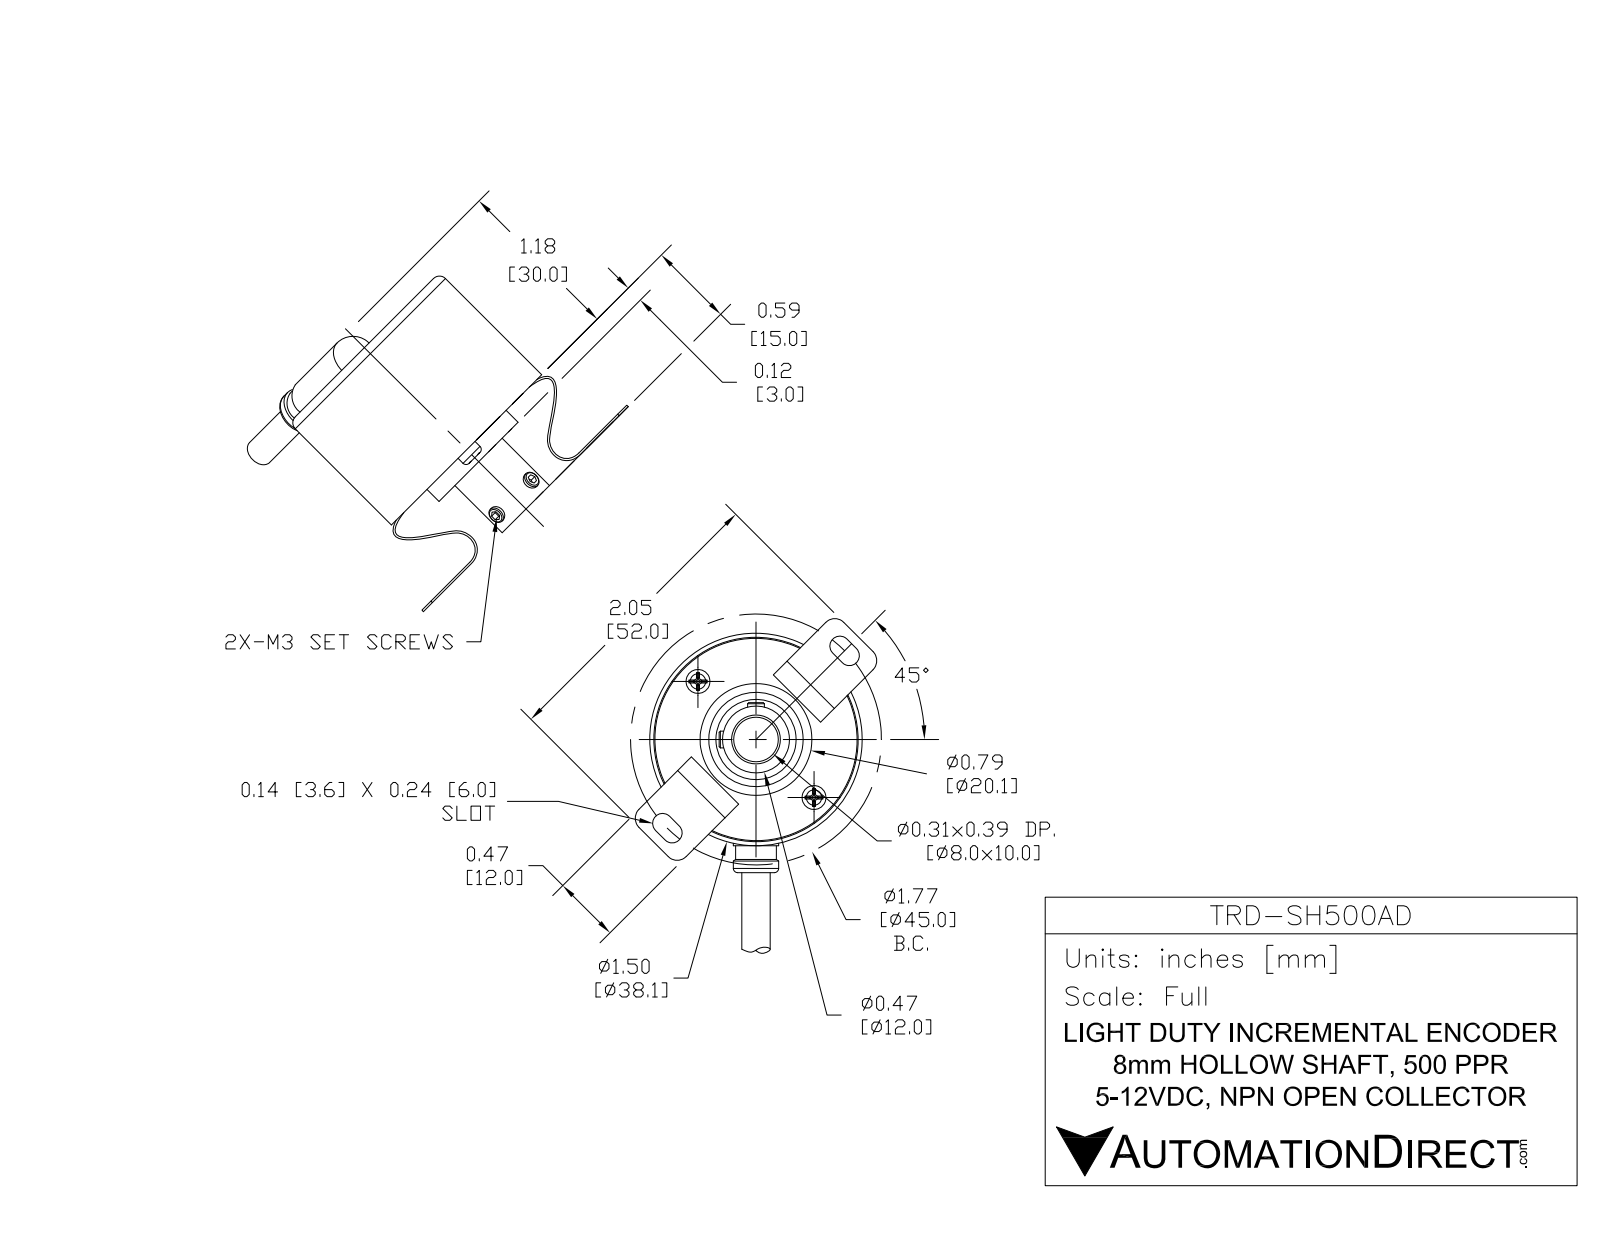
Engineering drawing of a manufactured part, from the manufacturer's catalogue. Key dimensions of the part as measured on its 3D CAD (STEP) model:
Part name (STEP PRODUCT): TRD-SH500AD
STEP written by: SolidWorks 2016 (AUTOMOTIVE_DESIGN)
Units: inches
Bodies: 11 solids, 322 faces (169 planar, 101 cylindrical, 52 other)
Overall size (bounding box): 3.952 × 1.772 × 1.684
Volume: 2.043 in³ · Surface area: 17.32 in²
Round holes (diameter × count): ⌀0.126 ×5, ⌀0.098 ×2, ⌀0.315 ×1, ⌀0.791 ×1
Round bosses / shafts (diameter × count): ⌀0.118 ×5, ⌀1.496 ×1, ⌀0.787 ×1, ⌀0.591 ×1, ⌀0.472 ×1, ⌀0.299 ×1, ⌀0.197 ×1, ⌀0.134 ×1
Partial cylindrical surfaces — rounded edges, fillets, slot ends (radius × count): R0.039 ×6, R0.118 ×5, R0.03 ×4, R0.071 ×4, R0.087 ×4, R0.098 ×4, R0.031 ×2, R0.146 ×2
Main face-to-face distances: 1.024, 0.579, 1.035, 0.591, 1.614, 1.602, 0.567, 0.118, 1.142, 0.106
Hole centre spacings: 0.551, 0.78, 0.955, 0.285, 0.285, 0.954, 1.065, 1.065
